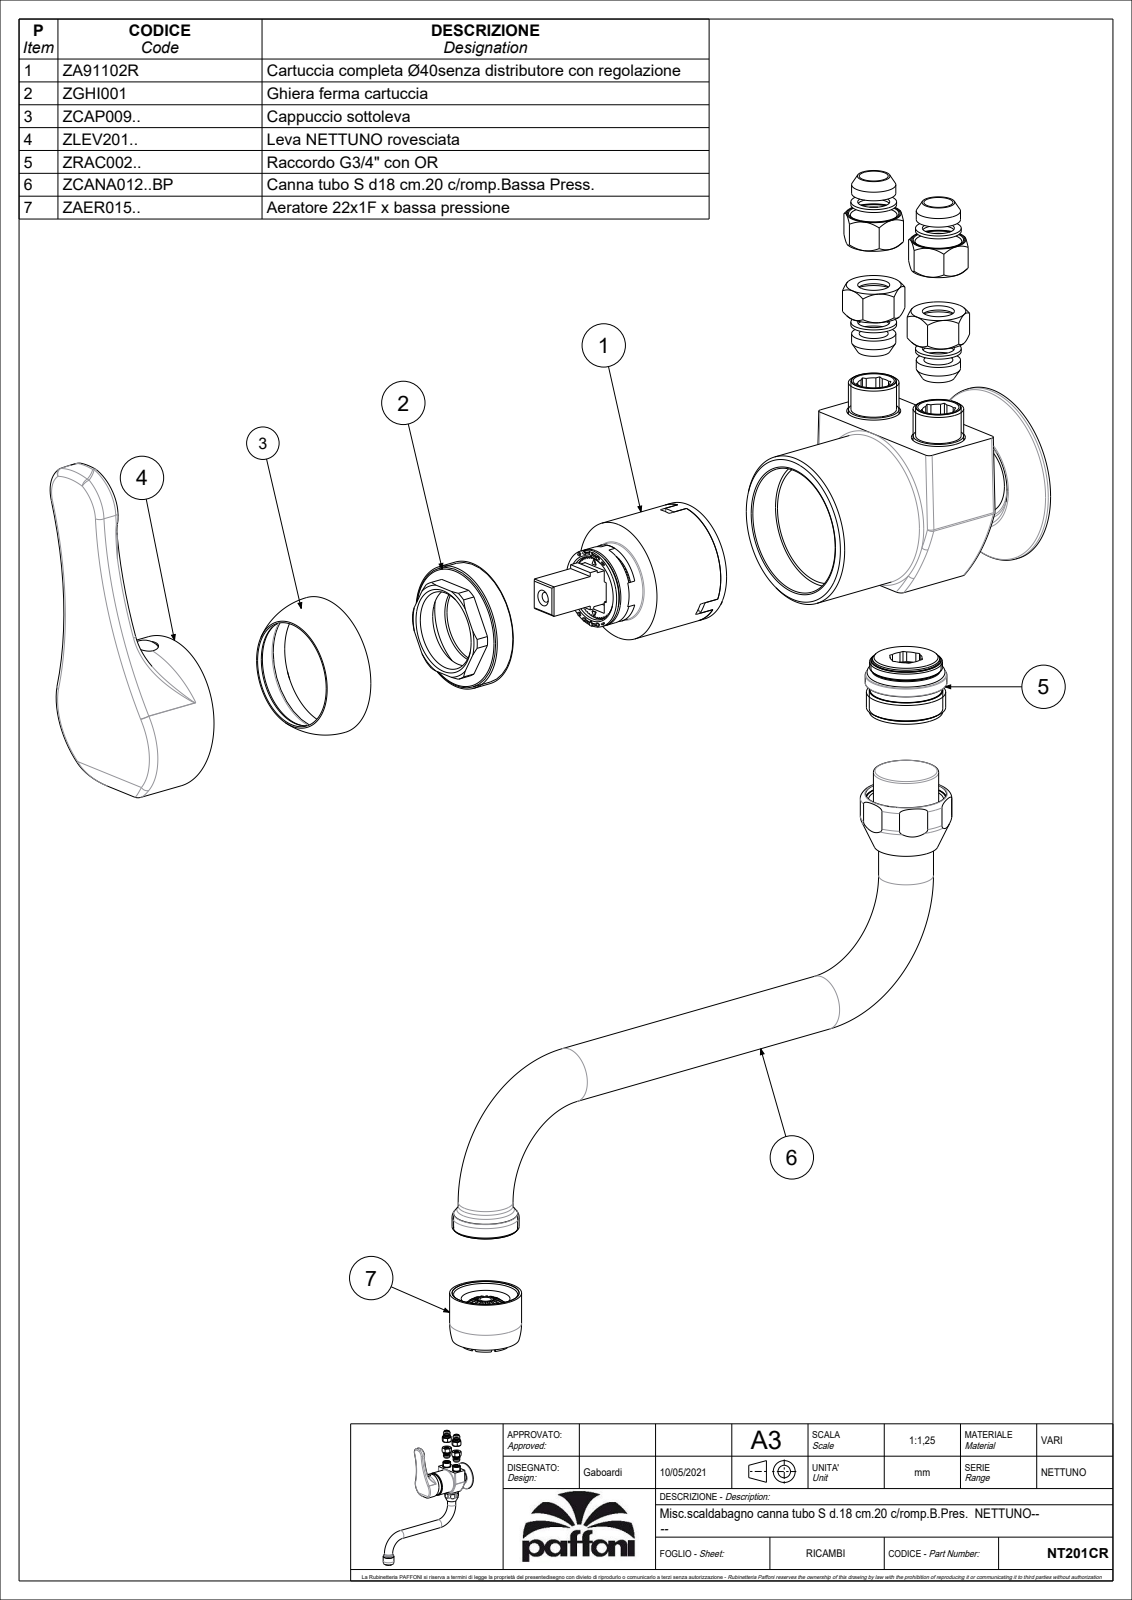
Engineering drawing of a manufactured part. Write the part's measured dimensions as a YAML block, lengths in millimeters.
part_name: "NT201CR"
step_written_by: "CREO PARAMETRIC BY PTC INC, 2020044 (CONFIG_CONTROL_DESIGN)"
units: millimeters
bodies: {solids: 2, faces: 1514, planar: 709, cylindrical: 437, other: 368}
overall_size: [248.88, 229.1, 58.8]
volume: 185838
surface_area: 113419
round_holes:
  - {diameter: 8, count: 4}
  - {diameter: 10.5, count: 4}
  - {diameter: 6, count: 3}
  - {diameter: 11, count: 3}
  - {diameter: 16.6, count: 3}
  - {diameter: 4, count: 2}
  - {diameter: 7, count: 2}
  - {diameter: 9.5, count: 2}
  - {diameter: 11.7, count: 2}
  - {diameter: 17.7, count: 2}
  - {diameter: 3, count: 1}
  - {diameter: 3.3, count: 1}
round_bosses_or_shafts:
  - {diameter: 18, count: 3}
  - {diameter: 50, count: 2}
  - {diameter: 23.5, count: 2}
  - {diameter: 22, count: 2}
  - {diameter: 16.6, count: 2}
  - {diameter: 5, count: 2}
  - {diameter: 58, count: 1}
  - {diameter: 39.5, count: 1}
partial_cylinders:
  - {radius: 0.2, count: 24}
  - {radius: 0.5, count: 22}
  - {radius: 5.86, count: 16}
  - {radius: 1, count: 13}
  - {radius: 2, count: 4}
  - {radius: 5.25, count: 2}
  - {radius: 70.5, count: 2}
  - {radius: 135, count: 2}
face_to_face_distances: [0.5, 5, 33.6, 28, 5.6, 18.3, 7.95, 2.95, 15, 55]
hole_center_spacings: [16.5, 33, 9.9, 0.5, 0.54, 1.51, 2, 8.6]
